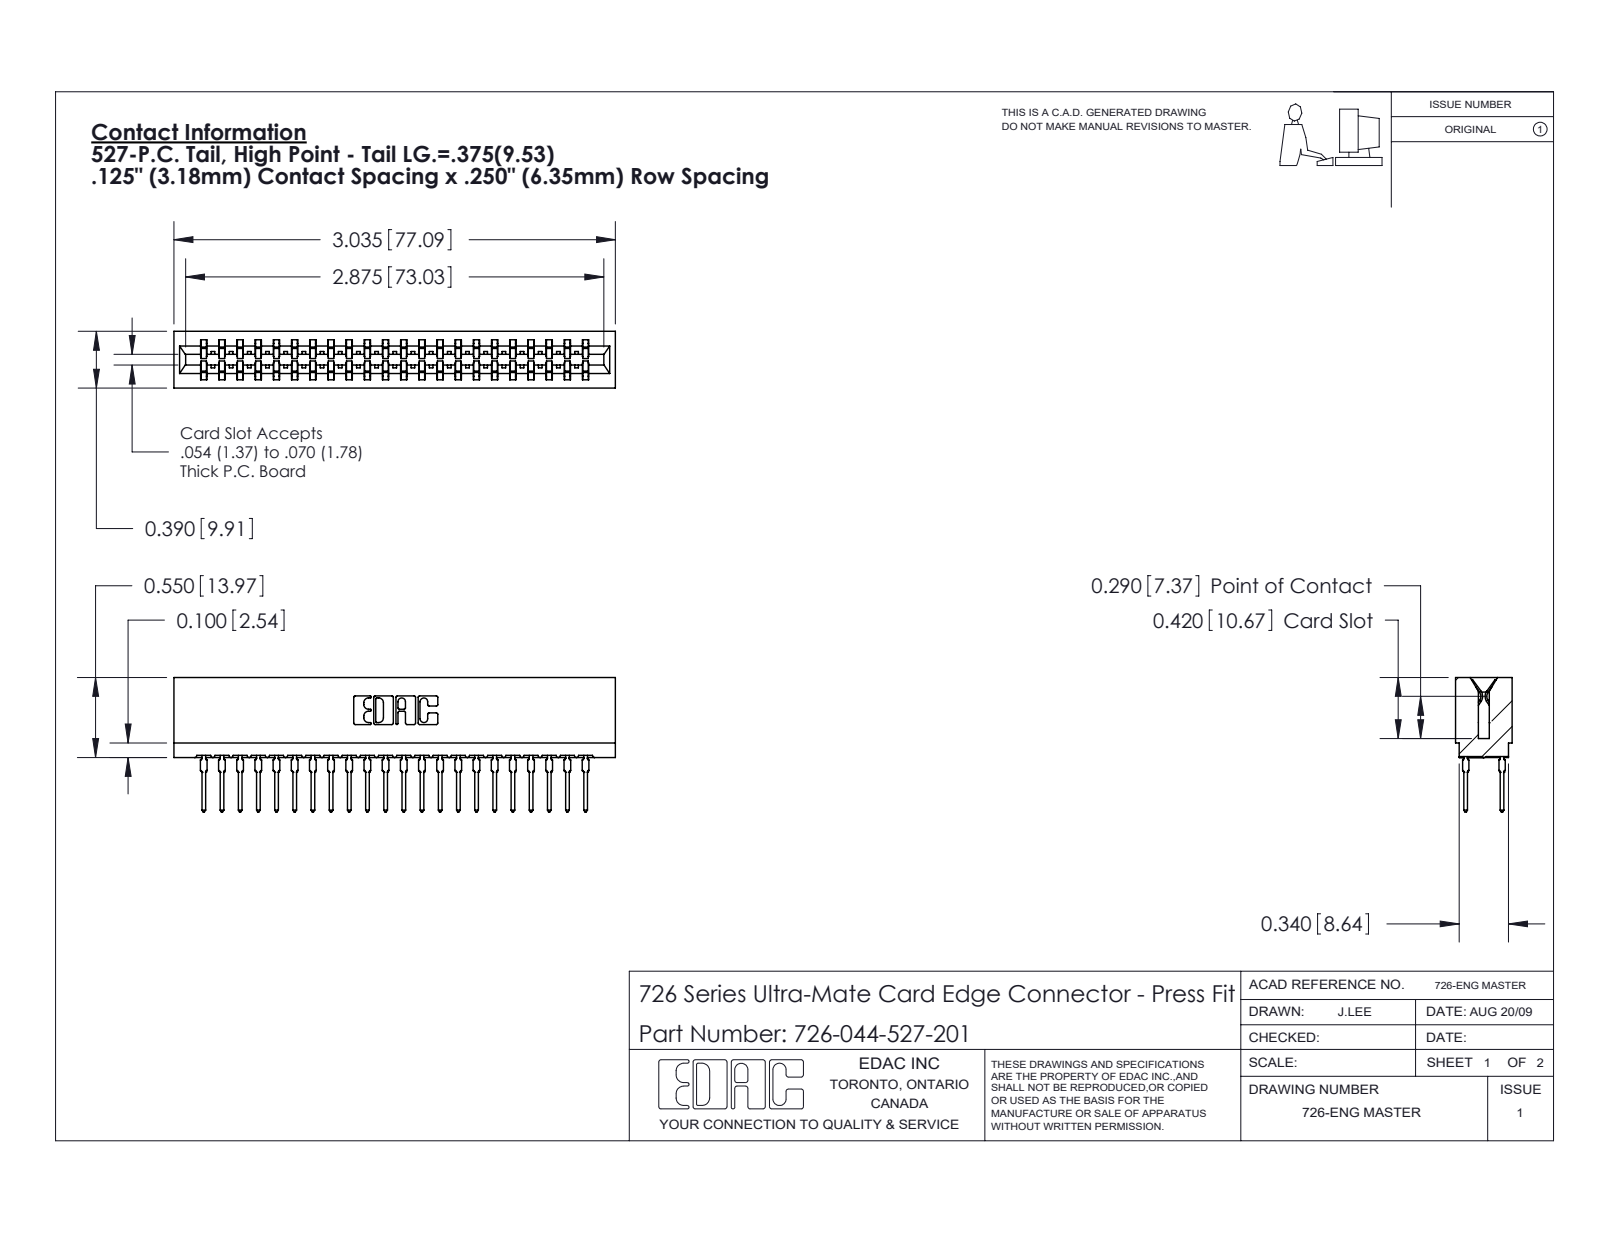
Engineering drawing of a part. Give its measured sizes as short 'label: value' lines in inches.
name: 726 Part_.515 Slot Depth - 01; 746-292-001_527; 726-044-527-201
written by: SolidWorks 2020 (CONFIG_CONTROL_DESIGN)
unit: in
bodies: 45 solids, 4035 faces (2079 planar, 812 cylindrical, 1144 other)
size: 3.035 × 0.924 × 0.39
volume: 0.444 in³; area: 18.77 in²
rounds: 88× R0.021, 23× R0.015, 22× R0.01, 8× R0.005, 8× R0.011, 6× R0.007, 6× R0.031, 3× R0.026
face distances: 0.057, 0.333, 0.025, 0.307, 0.39, 0.25, 0.083, 0.275, 0.042, 1.25
